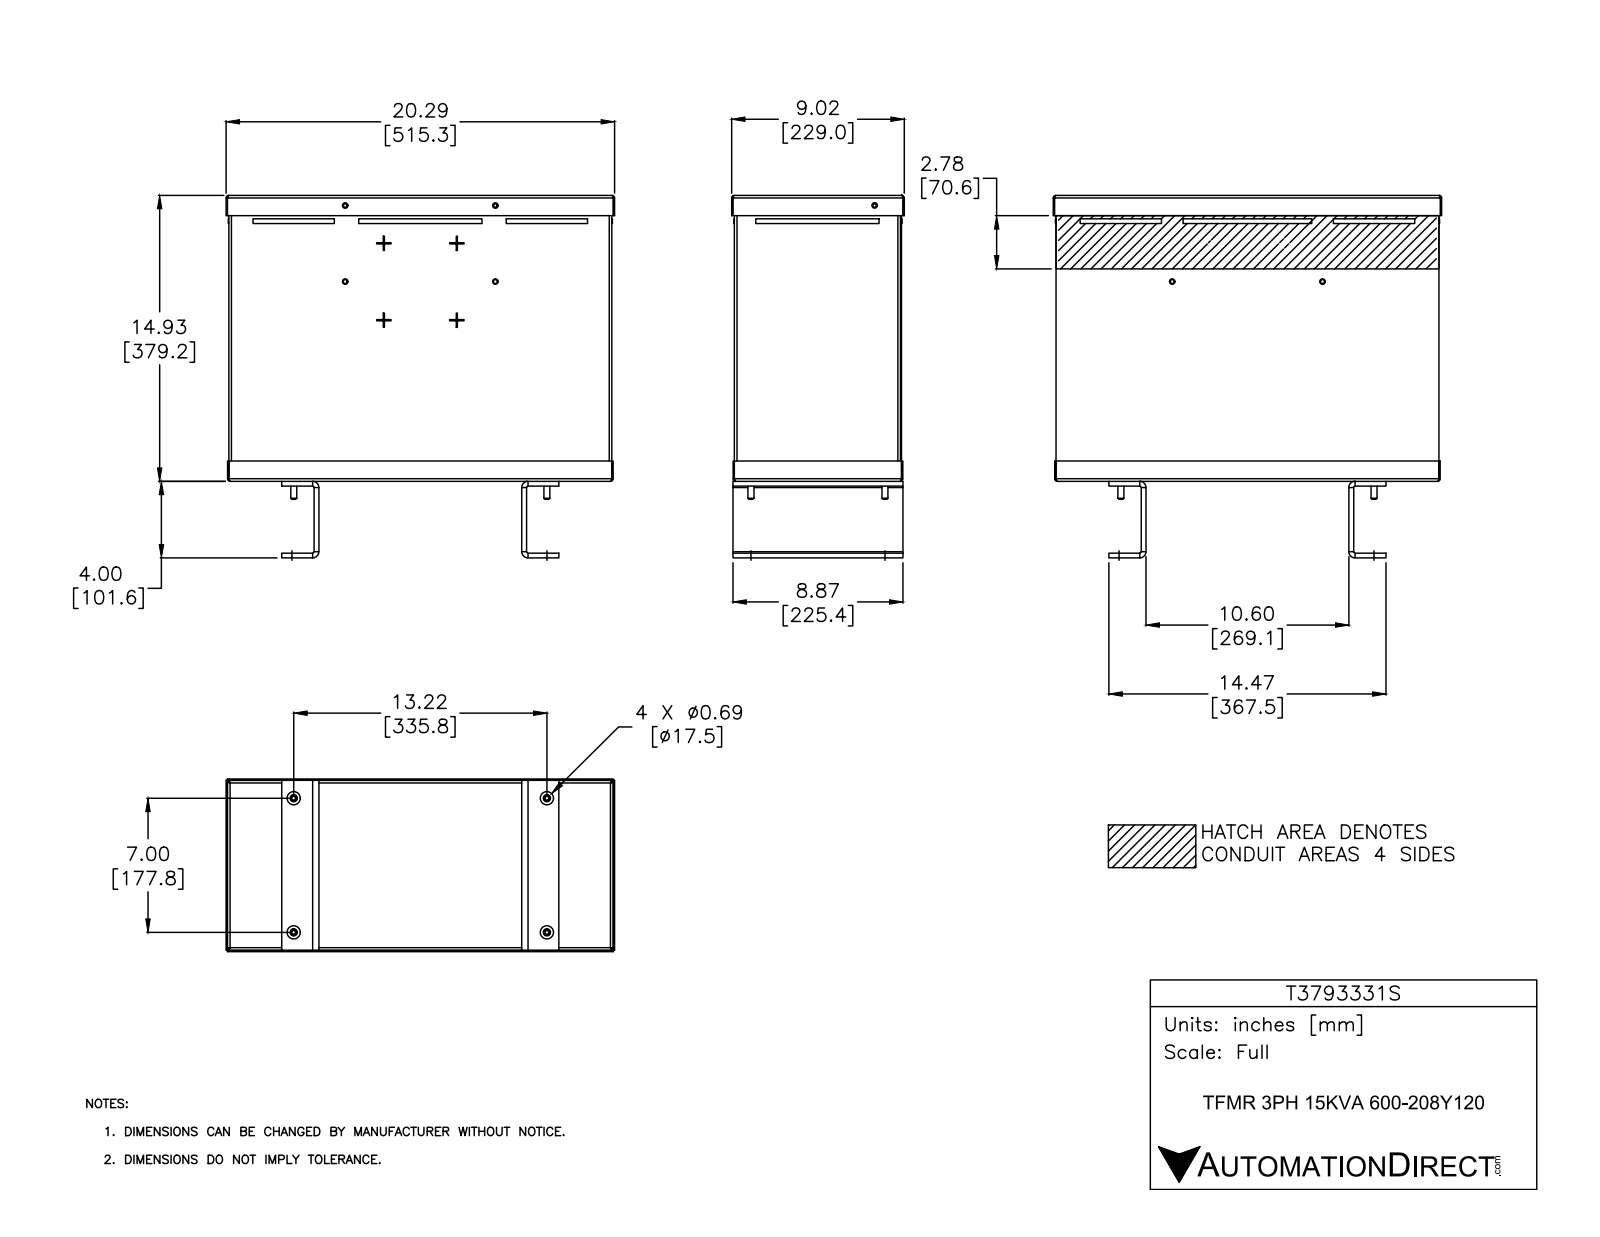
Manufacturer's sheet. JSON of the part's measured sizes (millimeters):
{"part_name": "T3793331S", "step_written_by": "SolidWorks 2015 (AUTOMOTIVE_DESIGN)", "units": "millimeters", "bodies": {"solids": 12, "faces": 474, "planar": 312, "cylindrical": 122, "other": 40}, "overall_size": [515.3, 480.8, 229], "volume_mm3": 1875000, "surface_area_mm2": 1977000, "round_holes": [[7.1, 8], [4.7, 5], [8, 4], [9.5, 4], [17.4, 4], [5.3, 2]], "round_bosses_or_shafts": [[7.9, 4]], "partial_cylinders_radius": [[1.9, 18], [3.4, 14], [2.4, 4], [3.1, 4], [8.3, 4]], "face_to_face_distances": [1.5, 220.2, 377.7, 218.7, 221.7, 506.5, 379.2, 376.1, 508, 505], "hole_center_spacings": [100.8, 100.8, 125.9, 177.8, 199.2, 223.3, 262.2, 301.7]}
